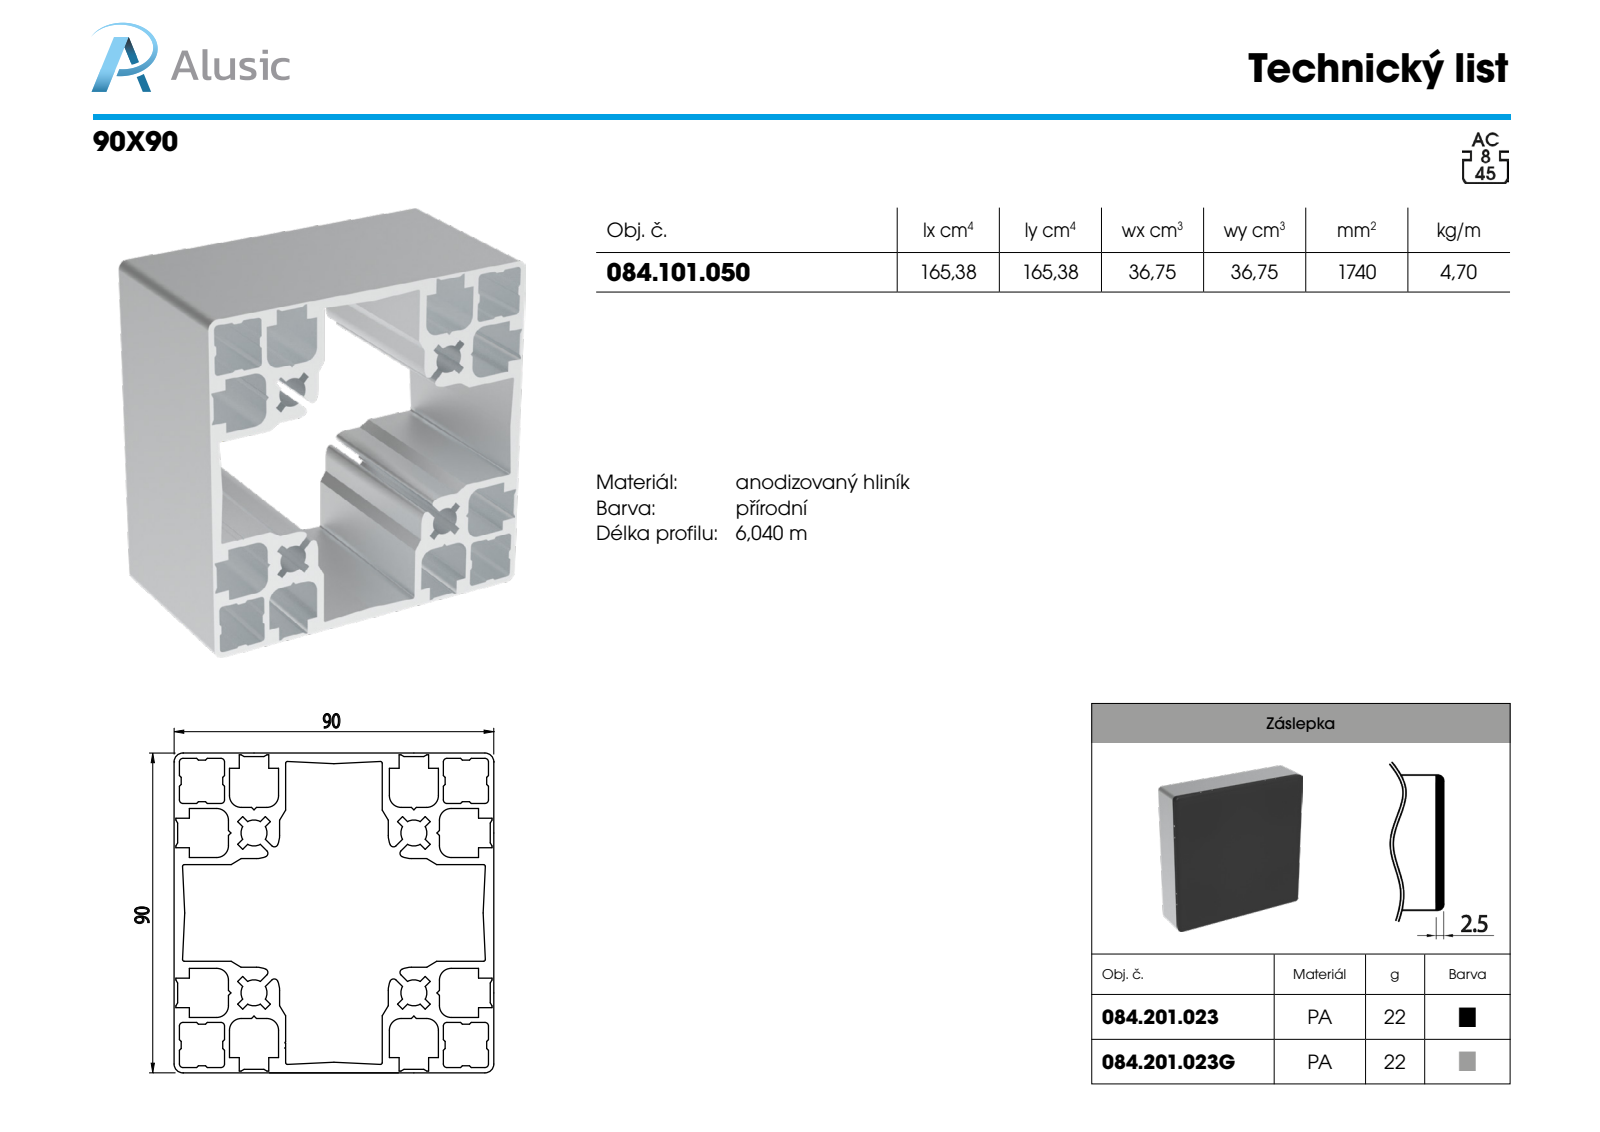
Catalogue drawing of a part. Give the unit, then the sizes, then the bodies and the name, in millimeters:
Units: millimetres
Overall size (bounding box): 100 × 90.01 × 90.01
Partial cylindrical surfaces — rounded edges, fillets, slot ends (radius × count): R1 ×24, R3.3 ×16, R0.5 ×8, R2.5 ×4, R3.65 ×4, R6.5 ×4, R0.2 ×1
Main face-to-face distances: 90.02, 90.01, 14.1, 2, 58.61, 31.41, 13.81, 59.11, 1.5, 14.2
Volume: 174 013 mm³ · Surface area: 150 258 mm²
Bodies: 1 solid, 371 faces (286 planar, 85 cylindrical, 0 other)
Part name (STEP PRODUCT): 084.101.050
STEP written by: SolidWorks 2018 (AUTOMOTIVE_DESIGN)
